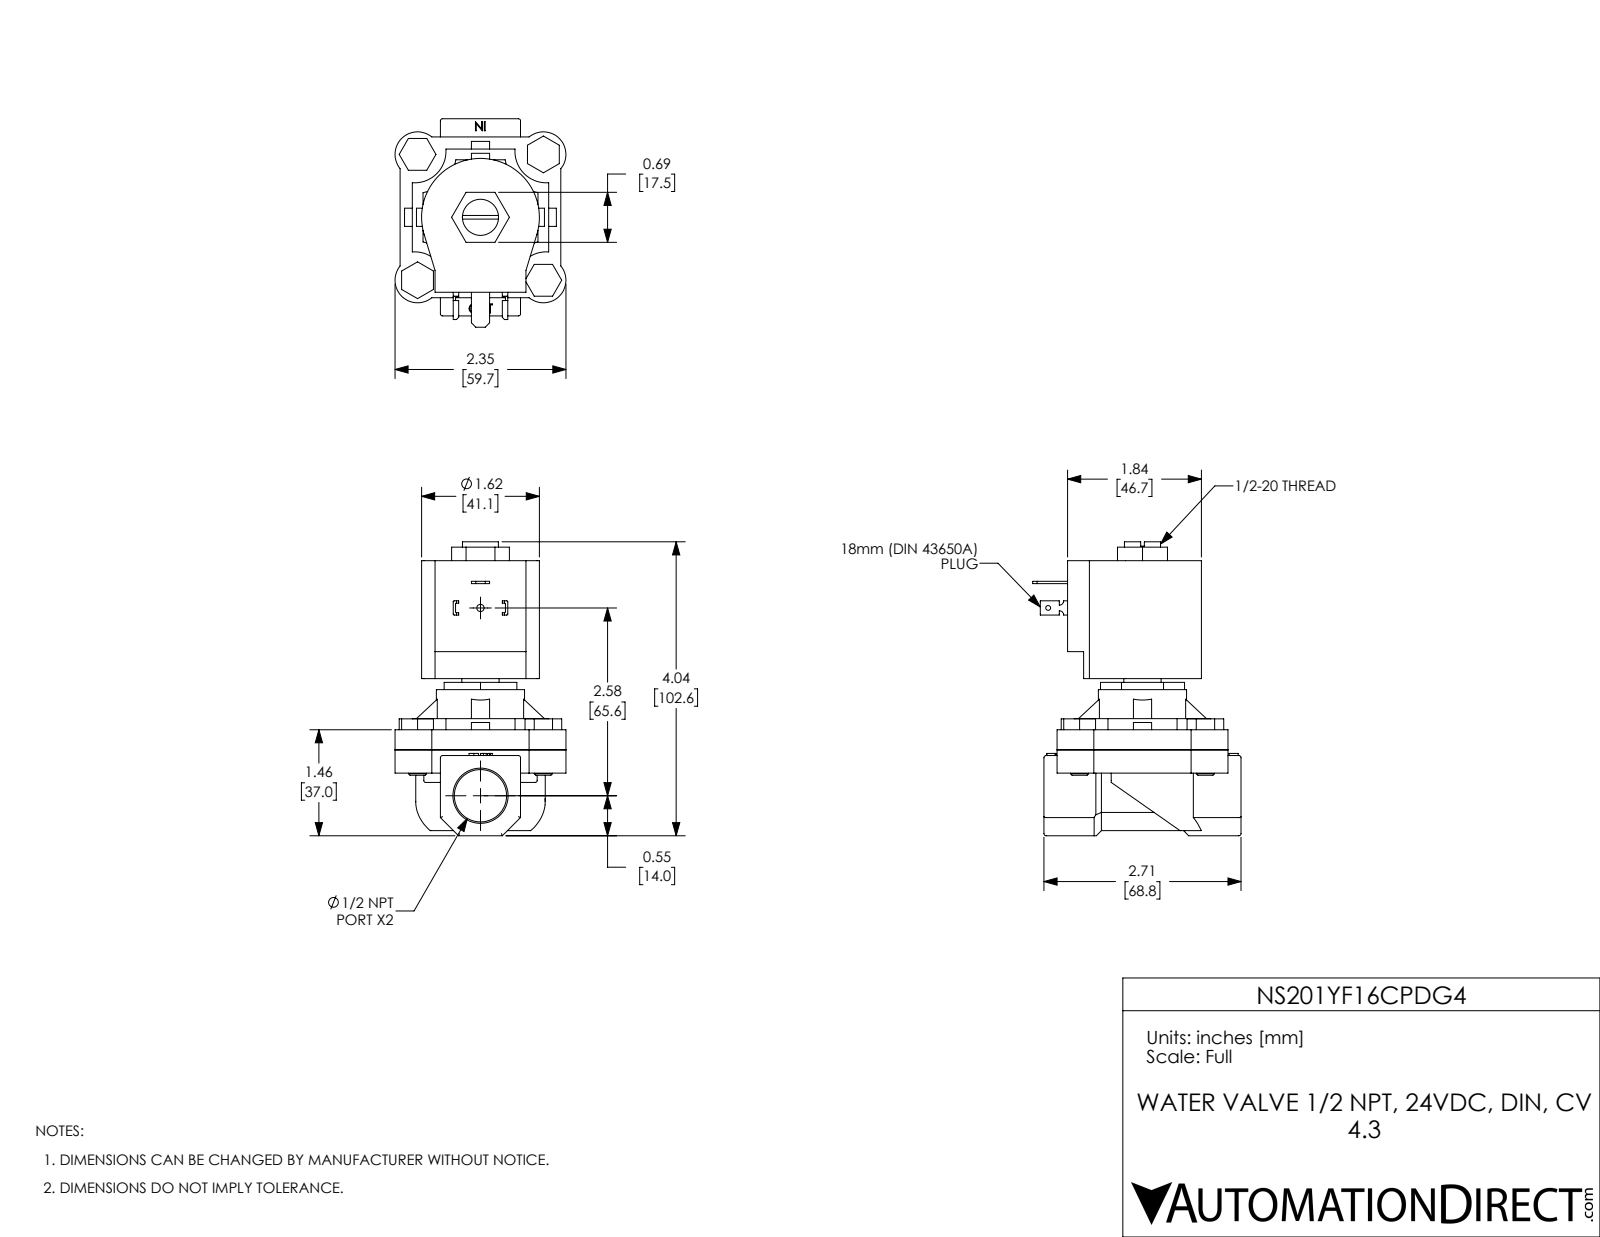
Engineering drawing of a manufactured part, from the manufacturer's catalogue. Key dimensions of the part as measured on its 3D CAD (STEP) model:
Part name (STEP PRODUCT): NS201YF16CPDG4
STEP written by: SolidWorks 2021 (CONFIG_CONTROL_DESIGN)
Units: inches
Bodies: 11 solids, 385 faces (239 planar, 113 cylindrical, 33 other)
Overall size (bounding box): 4.04 × 2.865 × 2.35
Volume: 10.1 in³ · Surface area: 67.71 in²
Round holes (diameter × count): ⌀0.25 ×4, ⌀0.067 ×1, ⌀0.1 ×1, ⌀0.496 ×1, ⌀0.512 ×1, ⌀0.719 ×1, ⌀1.155 ×1
Round bosses / shafts (diameter × count): ⌀0.248 ×4, ⌀1.213 ×1
Partial cylindrical surfaces — rounded edges, fillets, slot ends (radius × count): R0.03 ×15, R0.015 ×8, R0.31 ×4, R0.432 ×4, R0.579 ×4, R0.06 ×2, R0.81 ×1, R0.89 ×1
Main face-to-face distances: 0.276, 2.599, 2.323, 0.32, 0.596, 2.919, 0.554, 1.656, 0.25, 2.46
Hole centre spacings: 1.223, 1.73, 2.446, 2.581
